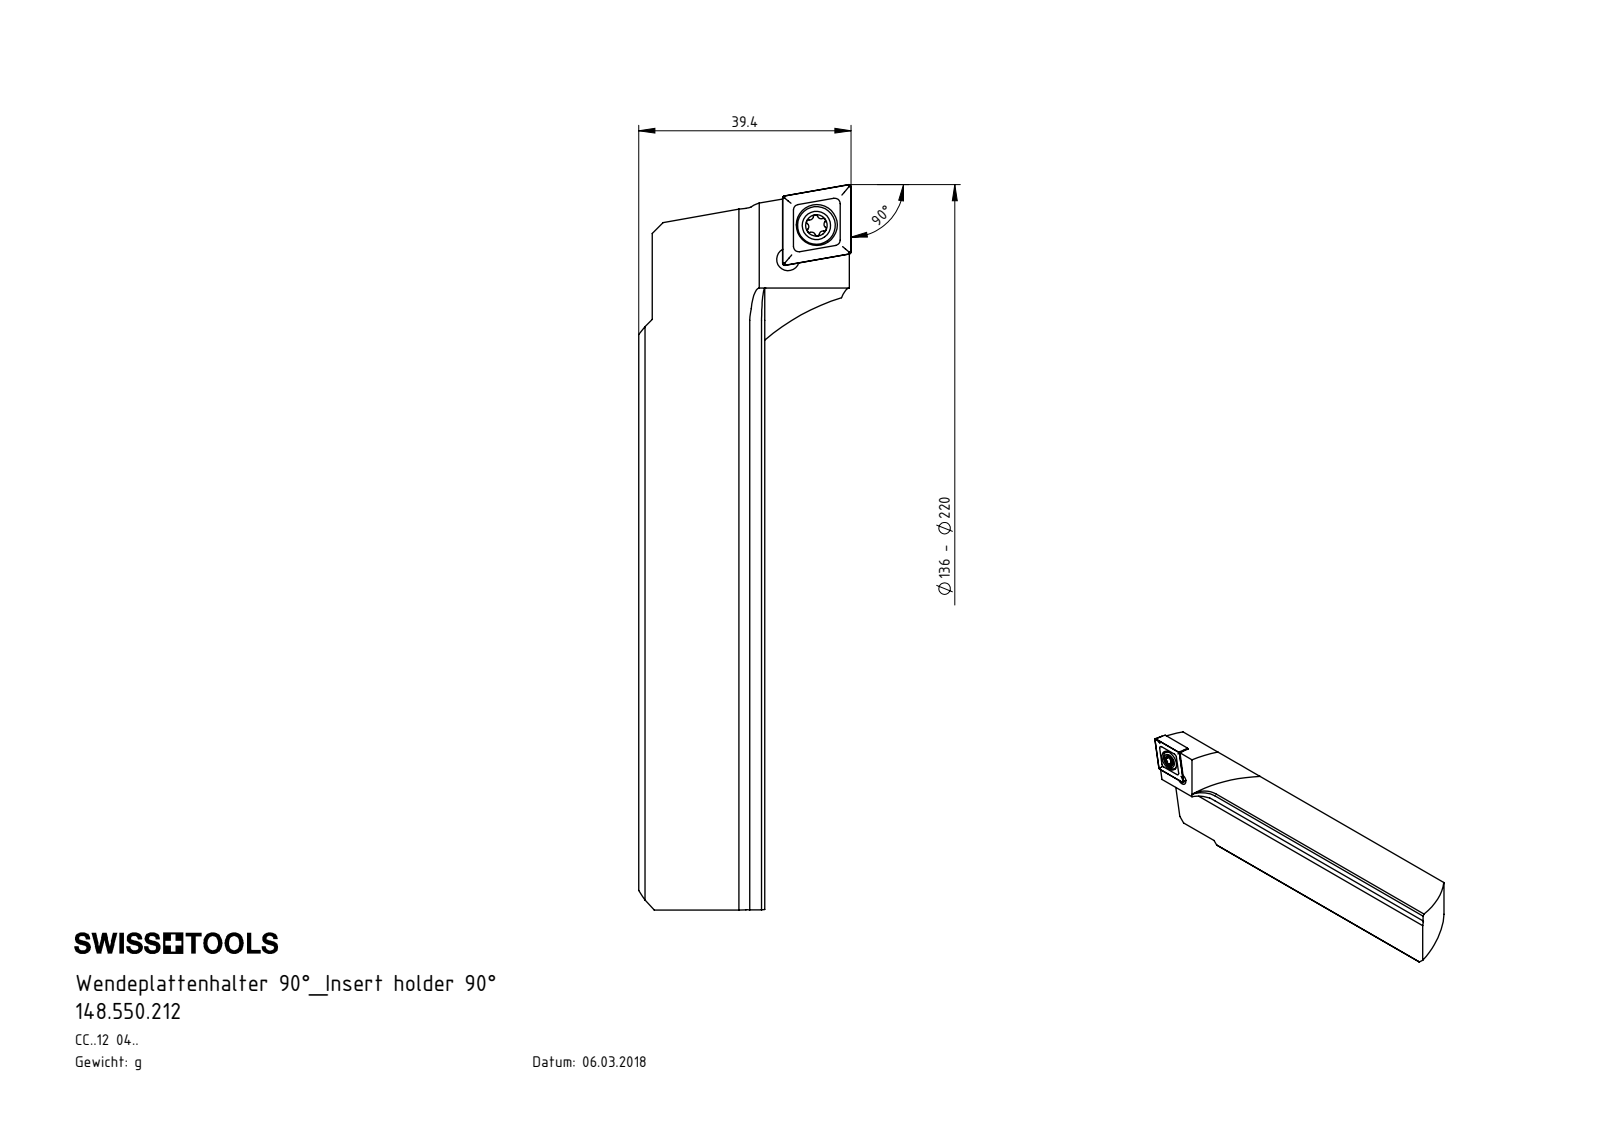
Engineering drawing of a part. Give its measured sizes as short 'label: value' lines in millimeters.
name: 148.550.212; F00-WCC.136.001_C; WCC-ER2.001.010_A; CCMT120404
written by: SolidWorks 2017 (CONFIG_CONTROL_DESIGN)
unit: mm
bodies: 3 solids, 556 faces (342 planar, 40 cylindrical, 174 other)
size: 134.59 × 39.4 × 27.35
volume: 55 816 mm³; area: 14 398 mm²
holes: 2× ⌀4.2, 1× ⌀5.5, 1× ⌀7.6
bosses: 1× ⌀7, 1× ⌀5
rounds: 8× R0.2, 6× R0.39, 4× R0.69, 3× R40, 2× R0.69, 1× R0.8, 1× R6
face distances: 2.38, 4.76, 21.3, 7.14, 9.52, 4.77, 7.15, 9.53, 11.91, 14.29
hole spacings: 8.21, 8.33
